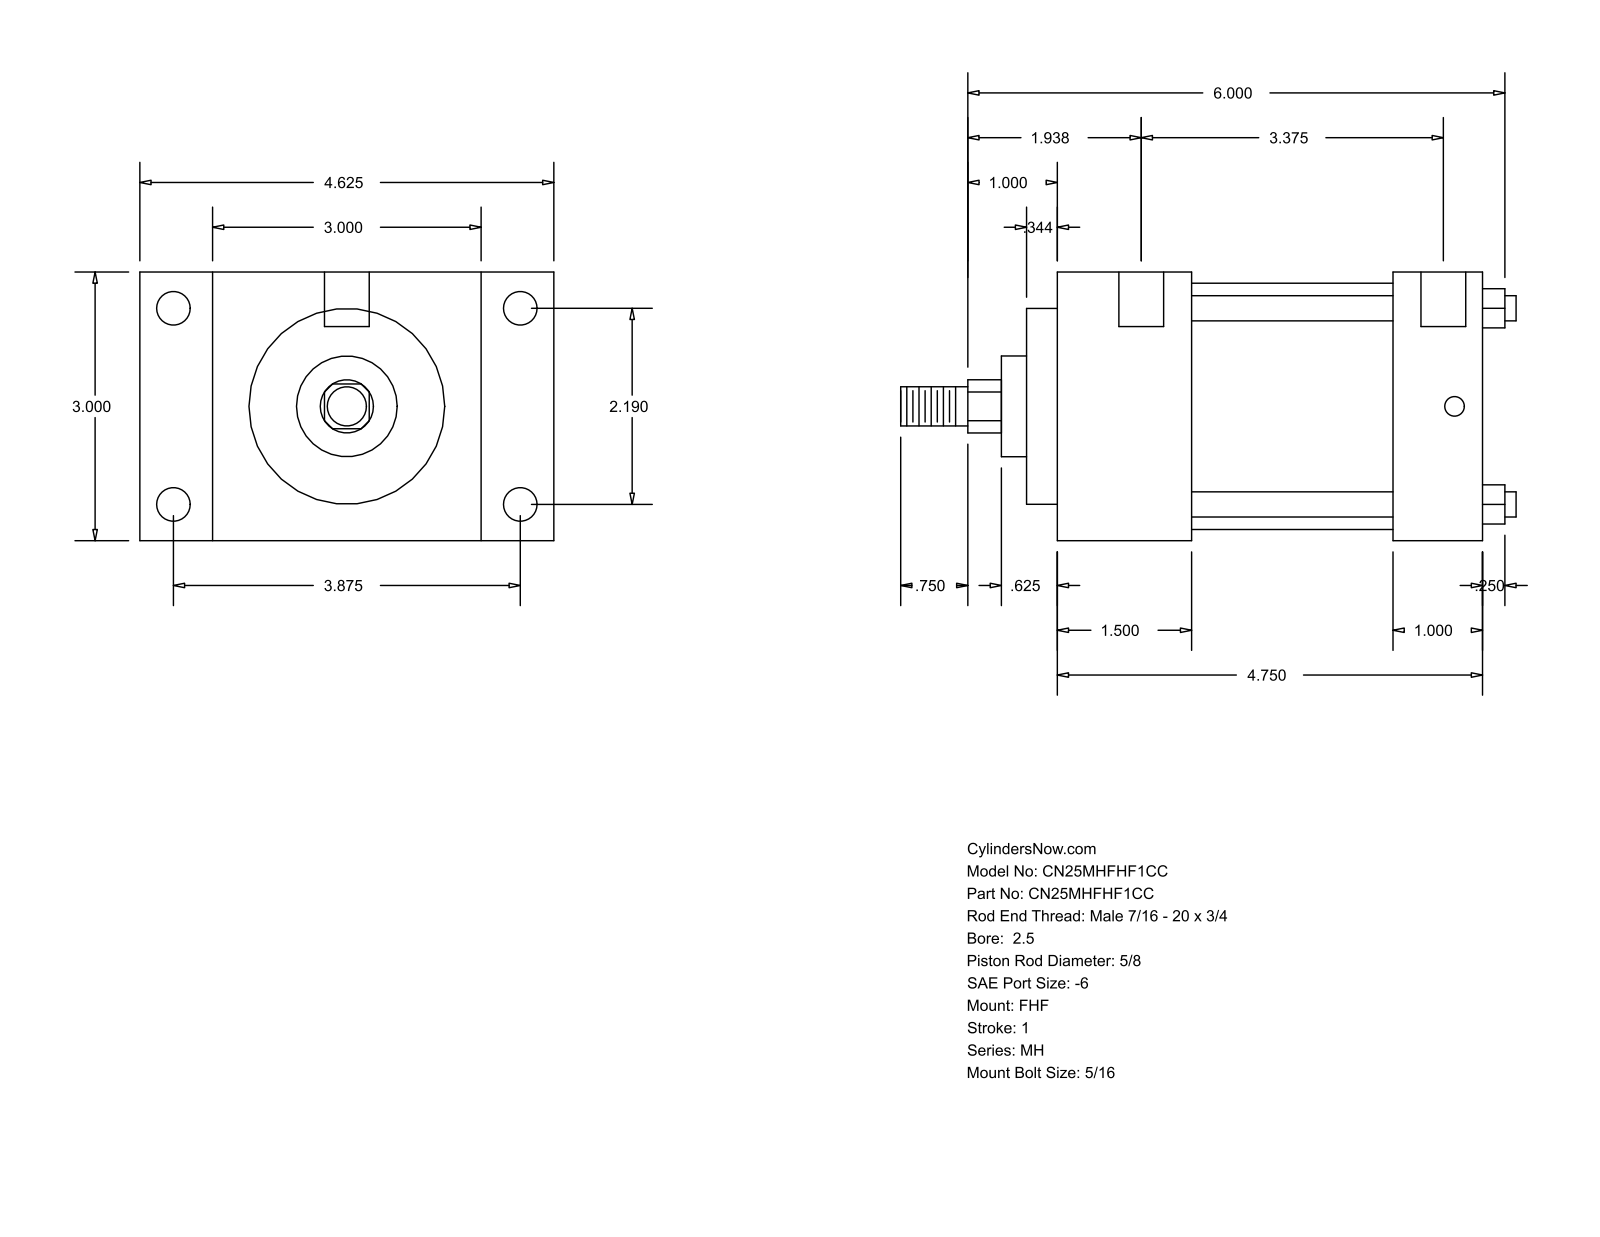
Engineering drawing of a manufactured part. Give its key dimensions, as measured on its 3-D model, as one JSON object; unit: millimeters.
{"part_name": "MH_FHF__0250_0.625", "step_written_by": "GSSL Pune (CONFIG_CONTROL_DESIGN)", "units": "millimeters", "bodies": {"solids": 0, "faces": 90, "planar": 61, "cylindrical": 29, "other": 0}, "overall_size": [174.62, 117.47, 76.2], "round_holes": [[5.56, 4], [9.53, 4], [12.7, 2]], "round_bosses_or_shafts": [[7.14, 4], [69.85, 1], [55.55, 1], [28.57, 1], [15.88, 1], [11.11, 1]], "partial_cylinders_radius": [[7.54, 1]], "face_to_face_distances": [76.2, 120.65, 82.55, 38.1, 20.64, 96.84, 117.48, 25.4, 57.15, 95.25], "hole_center_spacings": [55.62, 93.66, 98.42, 113.05, 3.17, 4.76, 85.73, 88.9]}
